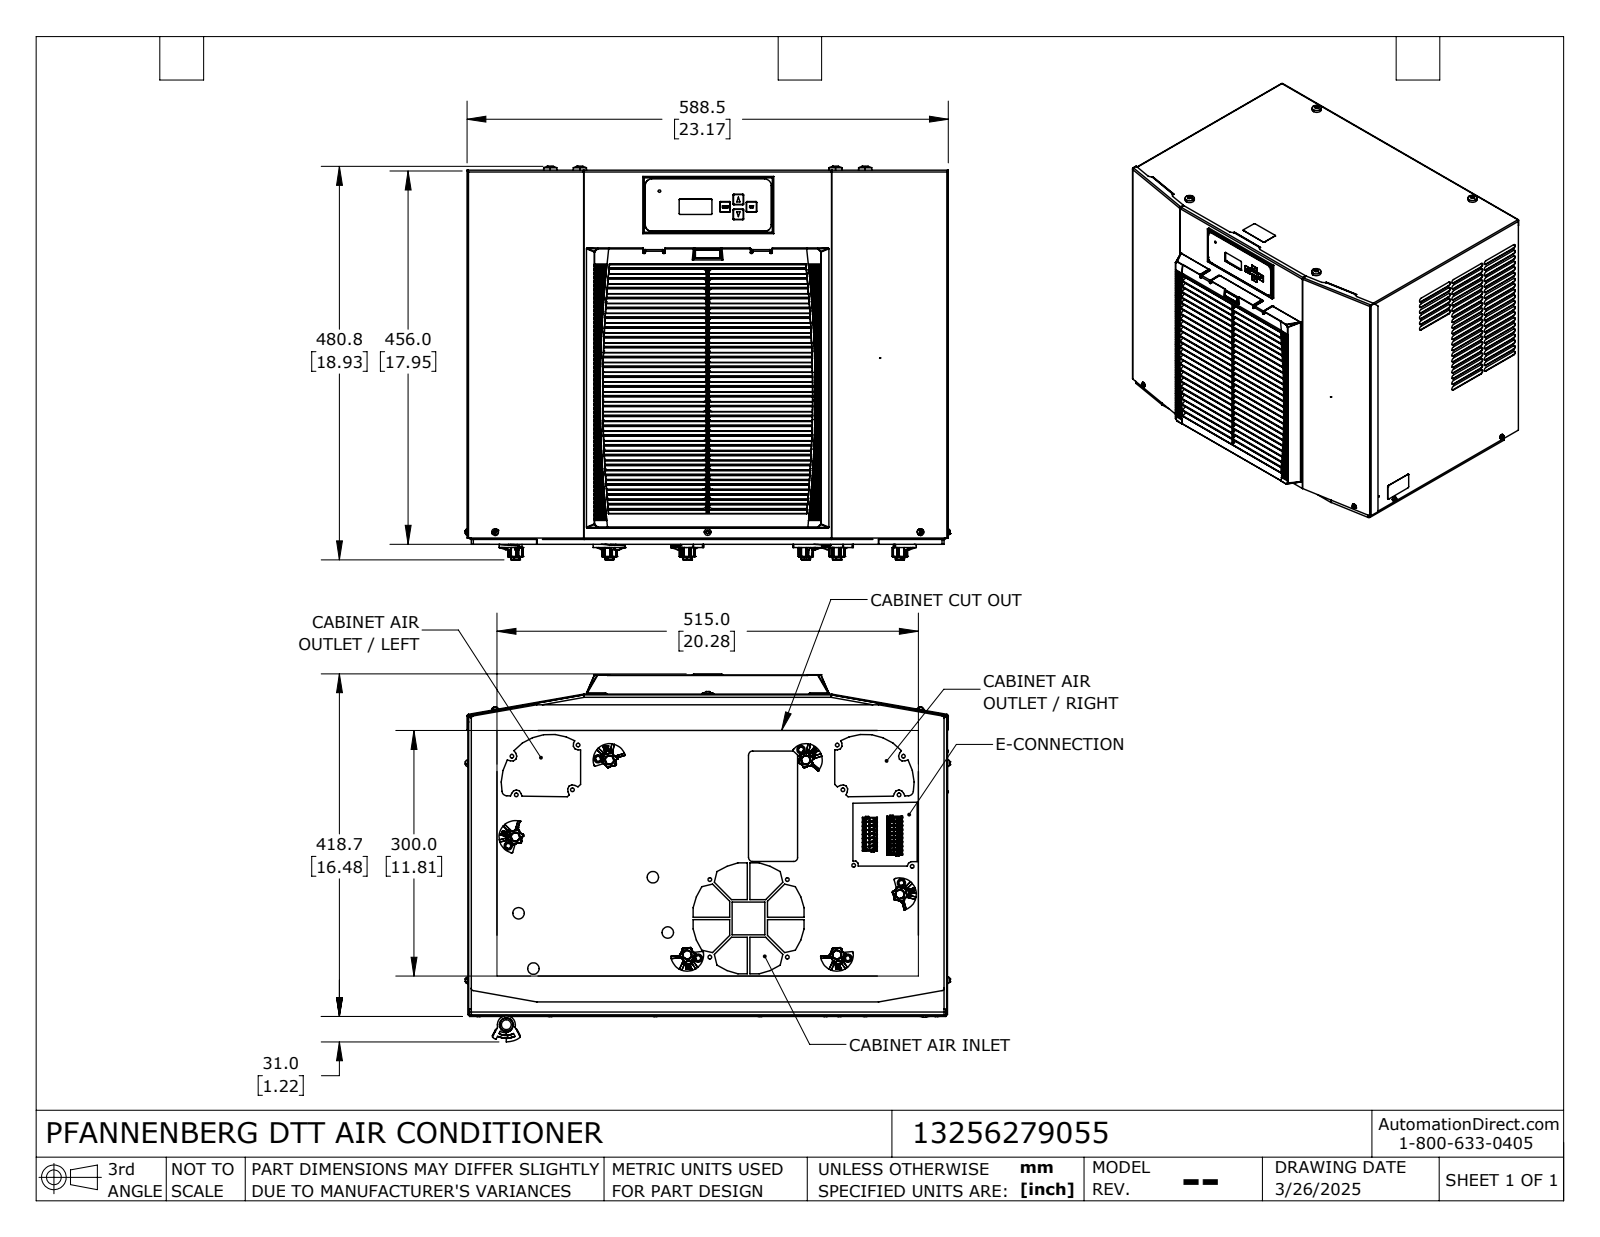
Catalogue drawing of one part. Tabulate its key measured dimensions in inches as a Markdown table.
| quantity | value |
| --- | --- |
| part name | 13256279055_Default |
| STEP written by | SolidWorks 2024 (CONFIG_CONTROL_DESIGN) |
| units | inches |
| bodies | 85 solids, 10572 faces (6279 planar, 2872 cylindrical, 1421 other) |
| overall size | 23.317 × 19.813 × 17.704 |
| volume | 6 206 in³ |
| surface area | 6 583 in² |
| round holes (diameter × count) | 0.091 × 26, 0.177 × 20, 0.165 × 13, 0.197 × 11, 0.236 × 7, 0.24 × 6, 0.272 × 6, 0.362 × 6, 0.138 × 5, 0.094 × 4, 0.217 × 4, 0.394 × 4 |
| round bosses / shafts (diameter × count) | 0.197 × 10, 0.157 × 9, 0.591 × 6, 0.465 × 6, 0.354 × 6, 0.63 × 5, 0.323 × 5, 0.165 × 5 |
| partial cylindrical surfaces (radius × count) | 0.157 × 504, 0.02 × 98, 0.008 × 78, 0.118 × 75, 0.039 × 65, 0.037 × 54, 0.004 × 48, 0.015 × 42 |
| main face-to-face distances | 0.039, 0.059, 23, 17.618, 0.079, 22.961, 23.039, 17.677, 17.657, 17.717 |
| hole center spacings | 3.731, 15.667, 0.02, 0.128, 0.25, 0.256, 0.635, 0.984 |
